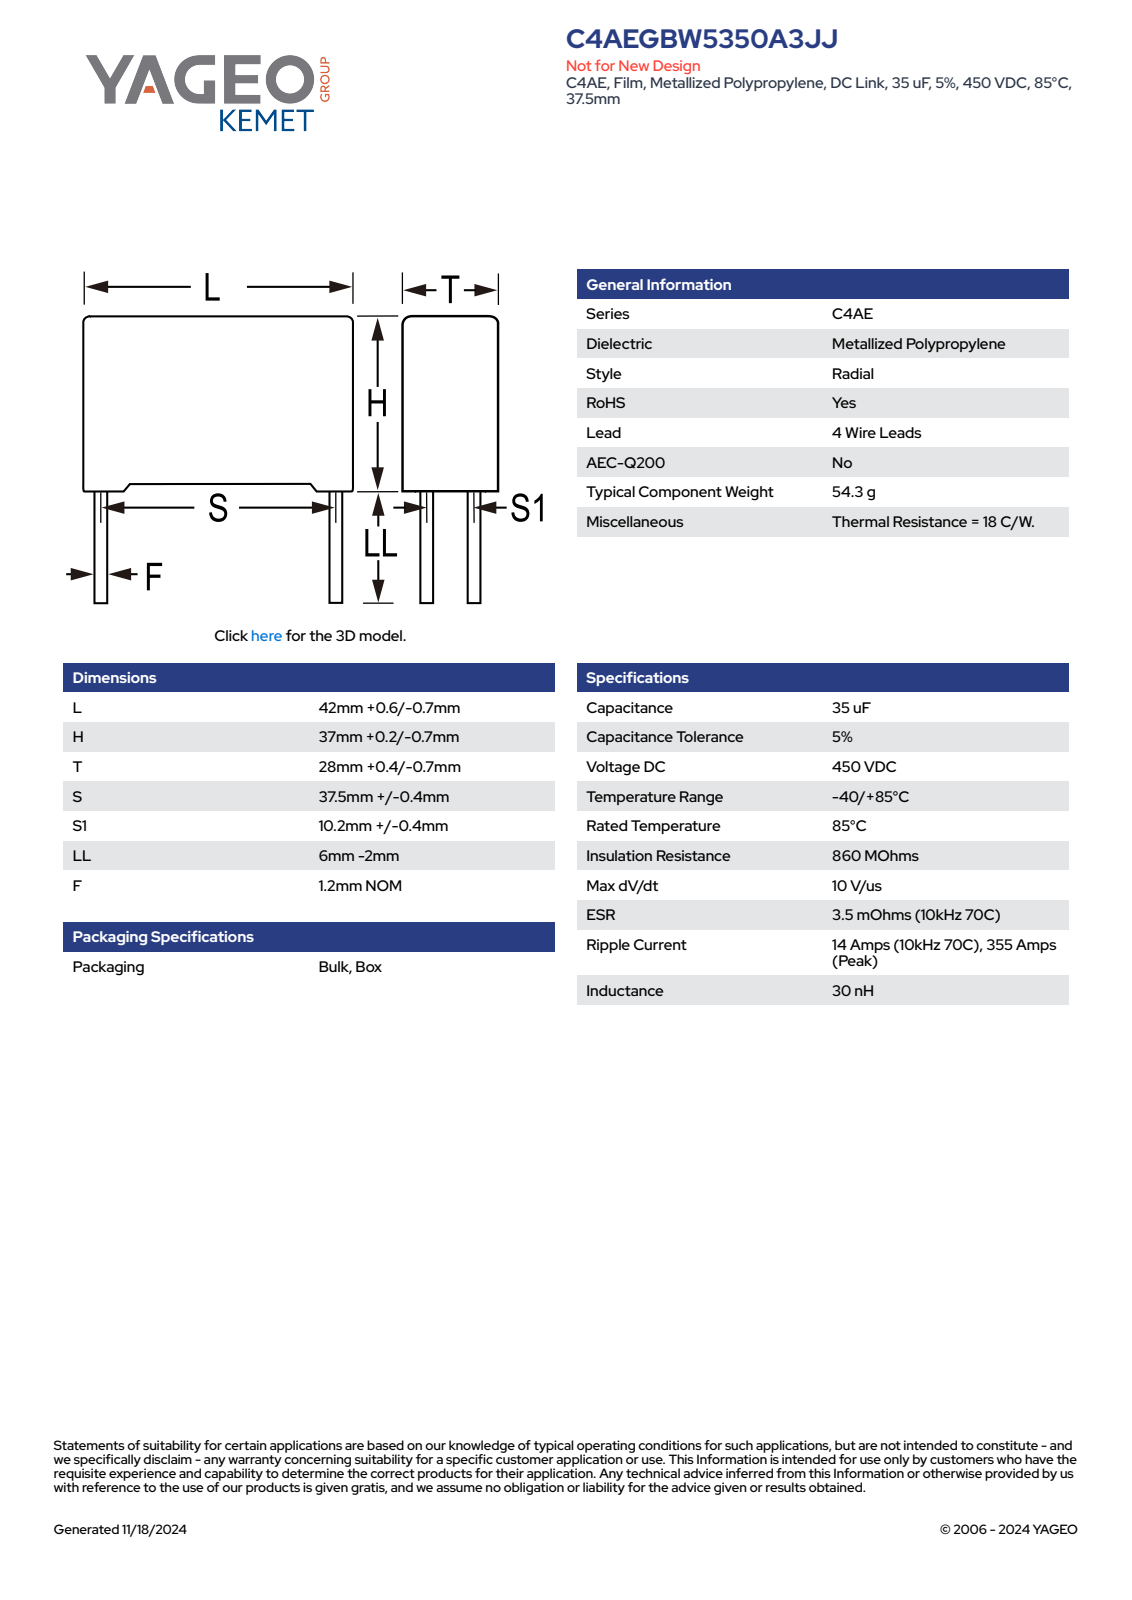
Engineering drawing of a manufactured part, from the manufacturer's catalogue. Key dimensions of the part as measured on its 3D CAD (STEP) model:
Part name (STEP PRODUCT): CFP_RB4_42.5X37X28_L42.6H37.2T28.4S37.5S110.2LL4F1.2
STEP written by: SolidWorks 2014 (AUTOMOTIVE_DESIGN)
Units: millimetres
Bodies: 4 solids, 87 faces (79 planar, 8 cylindrical, 0 other)
Overall size (bounding box): 42.6 × 41.2 × 28.41
Volume: 43 858 mm³ · Surface area: 7 918 mm²
Round bosses / shafts (diameter × count): ⌀1.2 ×4
Main face-to-face distances: 28.4, 36.11, 42.6, 1.09, 37.2, 1.75, 28.41, 40.85, 39.1, 26.65
